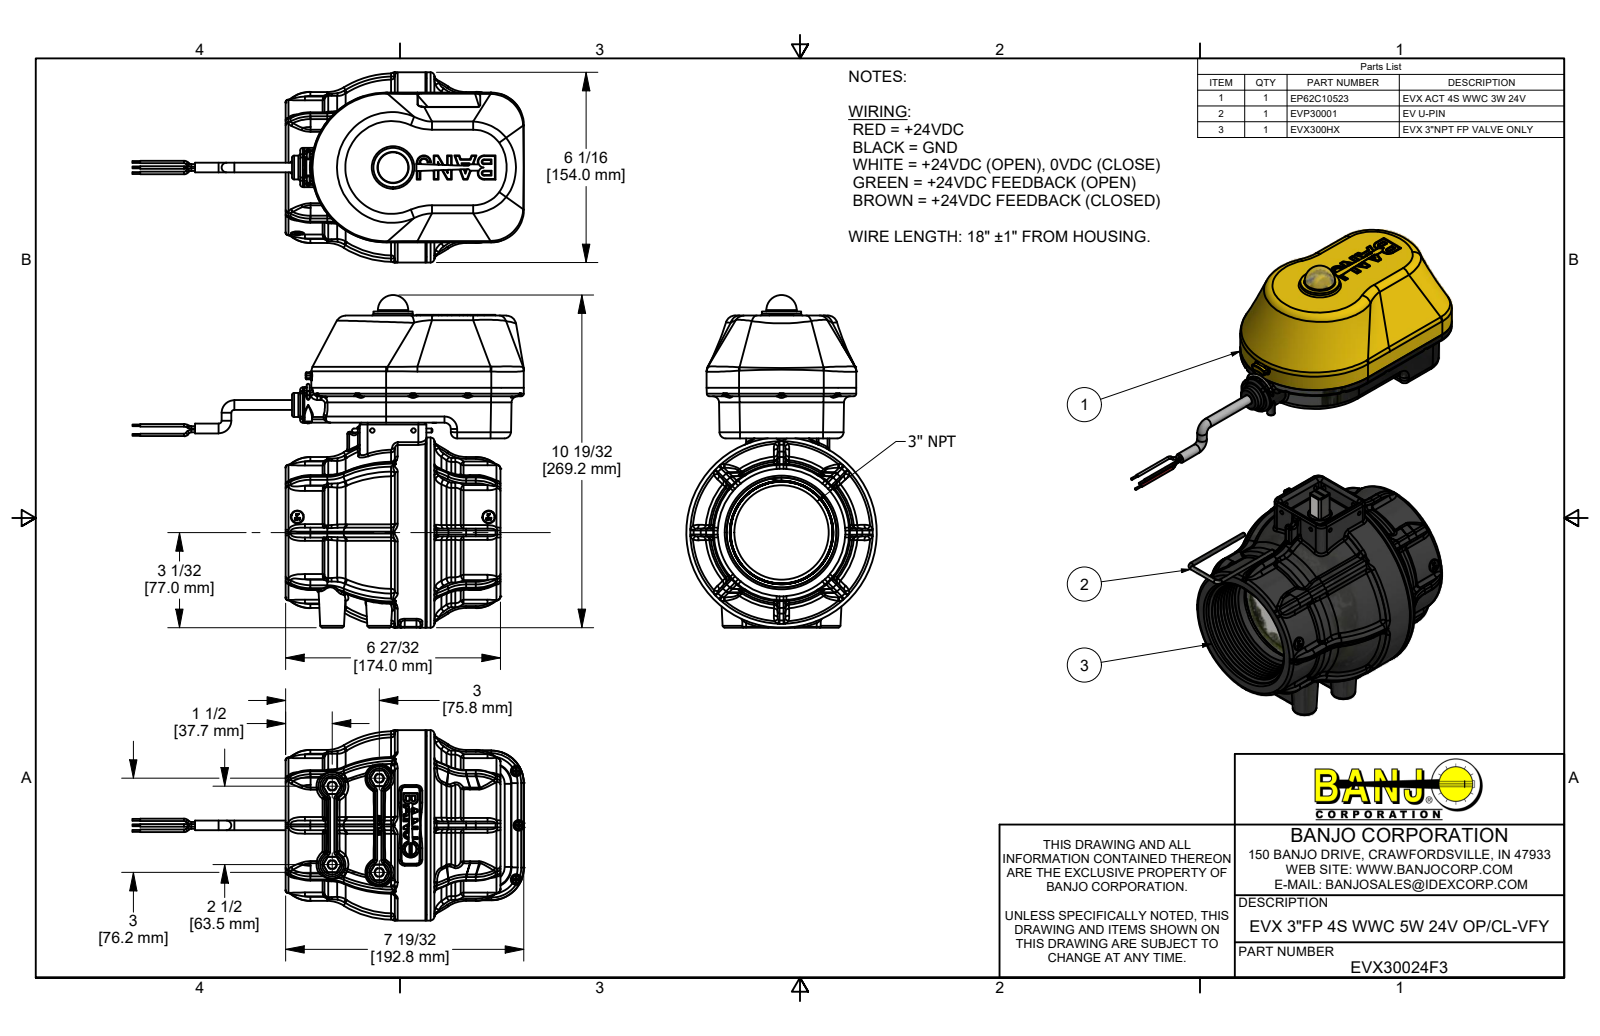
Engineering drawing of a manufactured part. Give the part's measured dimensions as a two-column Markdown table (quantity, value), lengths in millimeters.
| quantity | value |
| --- | --- |
| part name | EVX30024F3; EP62C10523; B61905PPHS; B632038PM (+8 more) |
| STEP written by | Autodesk Inventor 2019 (AUTOMOTIVE_DESIGN) |
| units | millimeters |
| bodies | 79 solids, 9076 faces (3067 planar, 3245 cylindrical, 2764 other) |
| overall size | 1555.9 × 269.2 × 154 |
| volume | 1 578 000 mm³ |
| surface area | 1 774 000 mm² |
| round holes (diameter × count) | 3.8 × 15, 2.4 × 11, 8.6 × 11, 2 × 7, 3.4 × 6, 2.6 × 4, 3.5 × 4, 3.8 × 4, 4.5 × 4, 6.7 × 4, 6.8 × 4, 11 × 4 |
| round bosses / shafts (diameter × count) | 6.4 × 19, 2 × 15, 3.6 × 11, 2.7 × 11, 2.2 × 11, 1.5 × 6, 11.1 × 4, 9.5 × 4 |
| partial cylindrical surfaces (radius × count) | 0.3 × 204, 10.3 × 138, 9.8 × 114, 7.8 × 112, 6.4 × 108, 15.5 × 106, 0.3 × 96, 3.2 × 74 |
| main face-to-face distances | 2.1, 12.7, 2.2, 3.2, 4.6, 2.4, 55.2, 57.7, 59.8, 58.4 |
| hole center spacings | 84.2, 57.7, 58.6, 61.6, 26.5, 33.4, 107.8, 108.9 |
